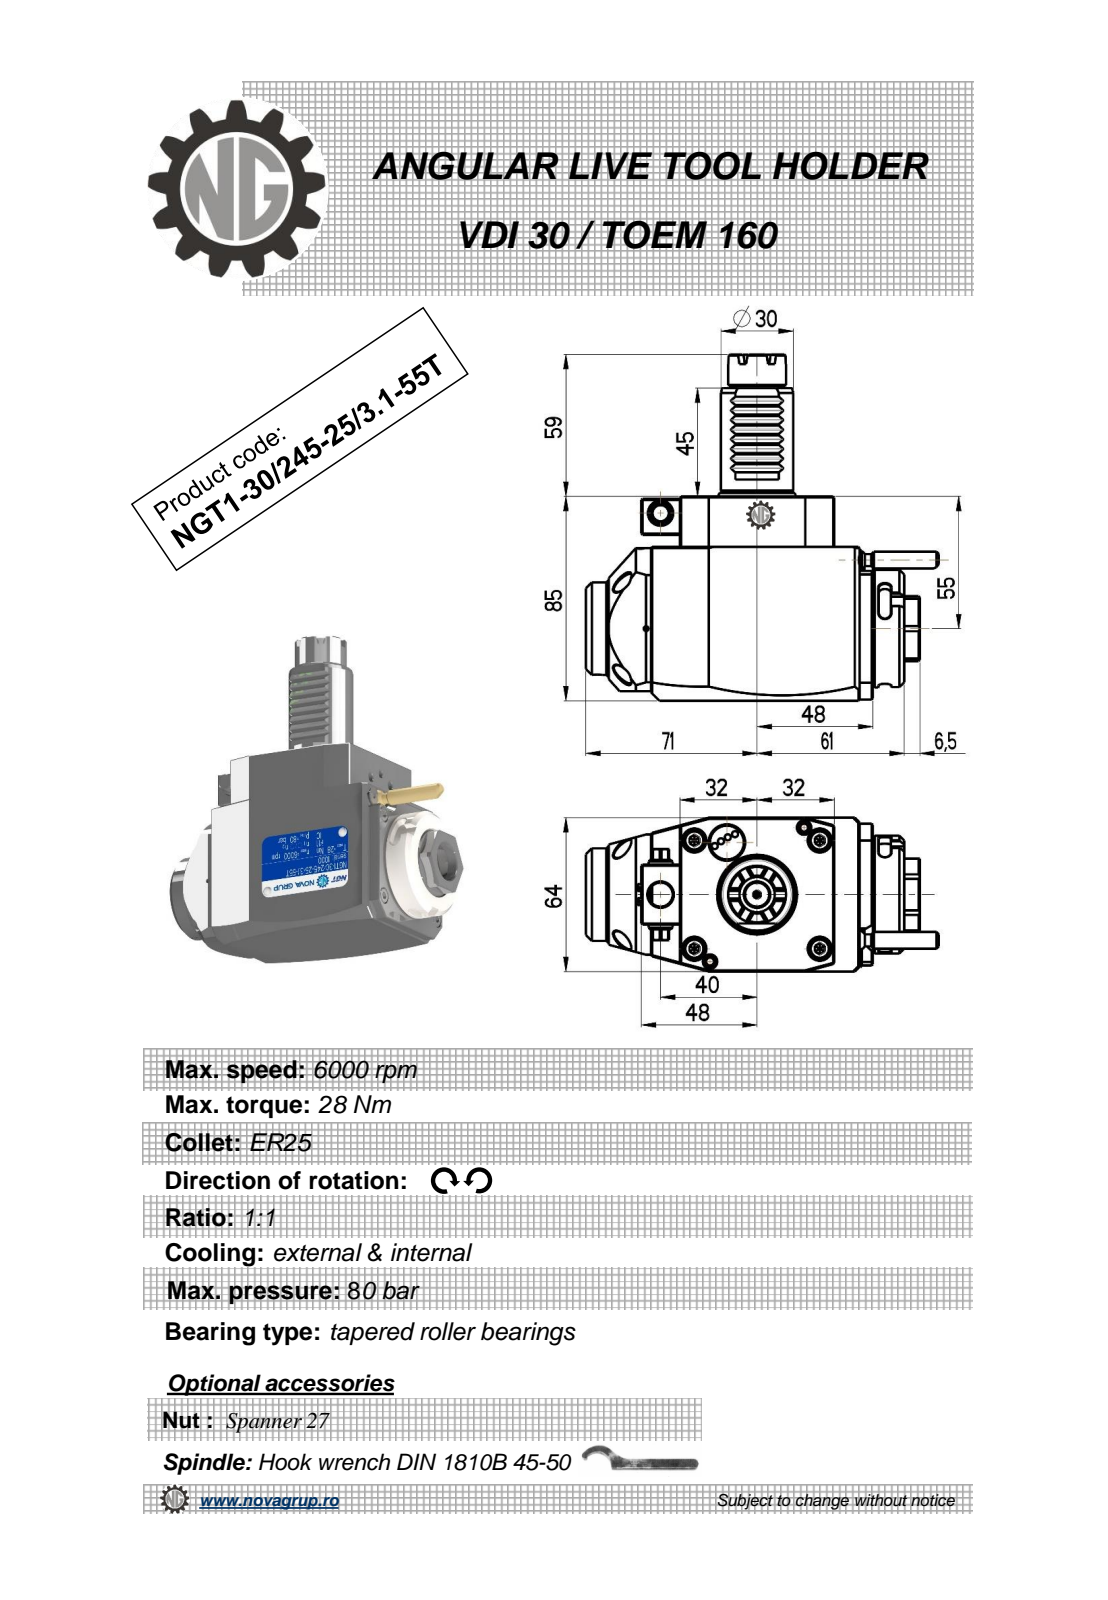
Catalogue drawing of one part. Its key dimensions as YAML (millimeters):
part_name: "NGT1_30_245_25_3_1_55T"
step_written_by: "PRO/ENGINEER BY PARAMETRIC TECHNOLOGY CORPORATION, 2010280 (CONFIG_CONTROL_DESIGN)"
units: millimeters
bodies: {solids: 1, faces: 380, planar: 212, cylindrical: 84, other: 84}
overall_size: [146.38, 144, 64]
volume: 563308
surface_area: 50992
round_holes:
  - {diameter: 2.5, count: 1}
  - {diameter: 3, count: 1}
  - {diameter: 8.5, count: 1}
  - {diameter: 9.5, count: 1}
  - {diameter: 10, count: 1}
  - {diameter: 18, count: 1}
round_bosses_or_shafts:
  - {diameter: 8, count: 2}
  - {diameter: 49, count: 1}
  - {diameter: 42, count: 1}
  - {diameter: 38.5, count: 1}
  - {diameter: 30, count: 1}
  - {diameter: 24, count: 1}
  - {diameter: 17.7, count: 1}
  - {diameter: 15.2, count: 1}
partial_cylinders:
  - {radius: 0.3, count: 8}
  - {radius: 2.5, count: 6}
  - {radius: 180, count: 2}
  - {radius: 3.85, count: 1}
  - {radius: 4.5, count: 1}
  - {radius: 15, count: 1}
  - {radius: 21.5, count: 1}
  - {radius: 33.5, count: 1}
face_to_face_distances: [64, 85, 16, 80, 13, 21, 29, 103, 119, 132]
hole_center_spacings: [26.17, 34.25, 46.5]
